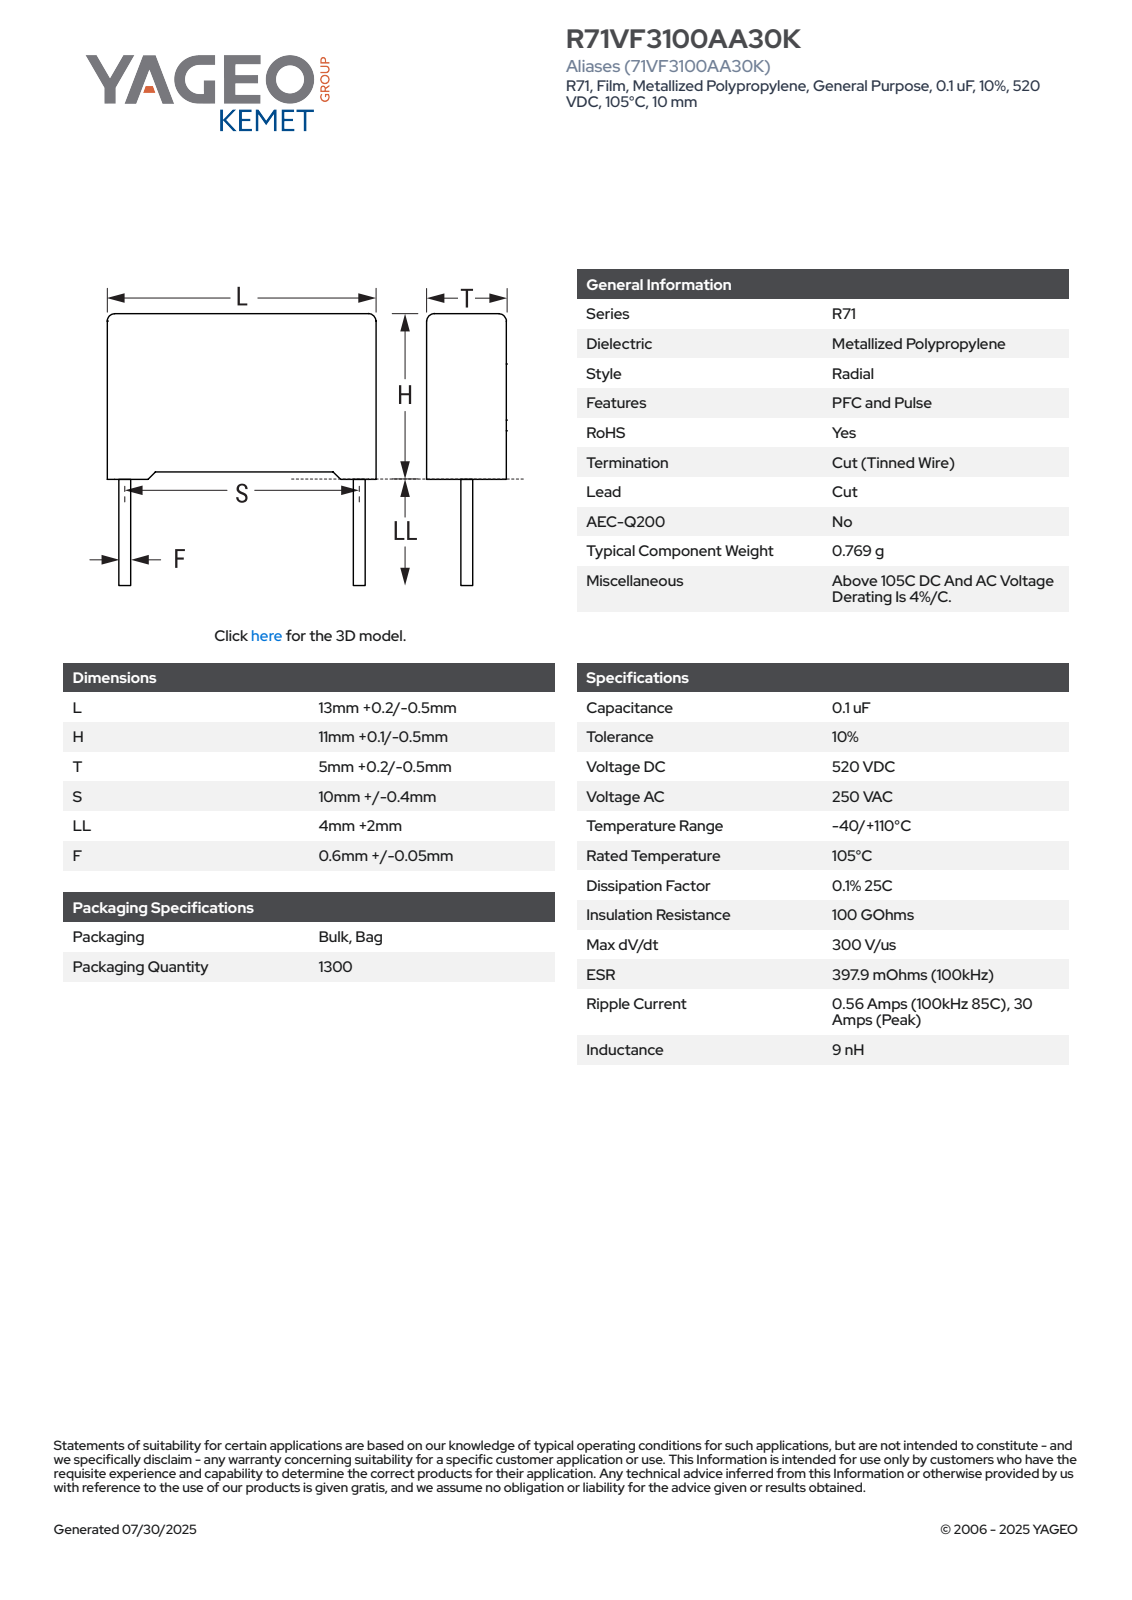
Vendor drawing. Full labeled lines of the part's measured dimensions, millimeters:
Part name (STEP PRODUCT): CFR_RB2_13X11X5_L13.2H11.1T5.2S10LL6F0.65
STEP written by: SolidWorks 2021 (AUTOMOTIVE_DESIGN)
Units: millimetres
Bodies: 4 solids, 85 faces (77 planar, 8 cylindrical, 0 other)
Overall size (bounding box): 17.1 × 13.2 × 5.21
Volume: 722 mm³ · Surface area: 594 mm²
Round bosses / shafts (diameter × count): ⌀0.65 ×2
Partial cylindrical surfaces — rounded edges, fillets, slot ends (radius × count): R0.5 ×4
Main face-to-face distances: 5.2, 13.2, 10.35, 0.44, 4.76, 0.75, 11.1, 4.32, 12.76, 0.37
